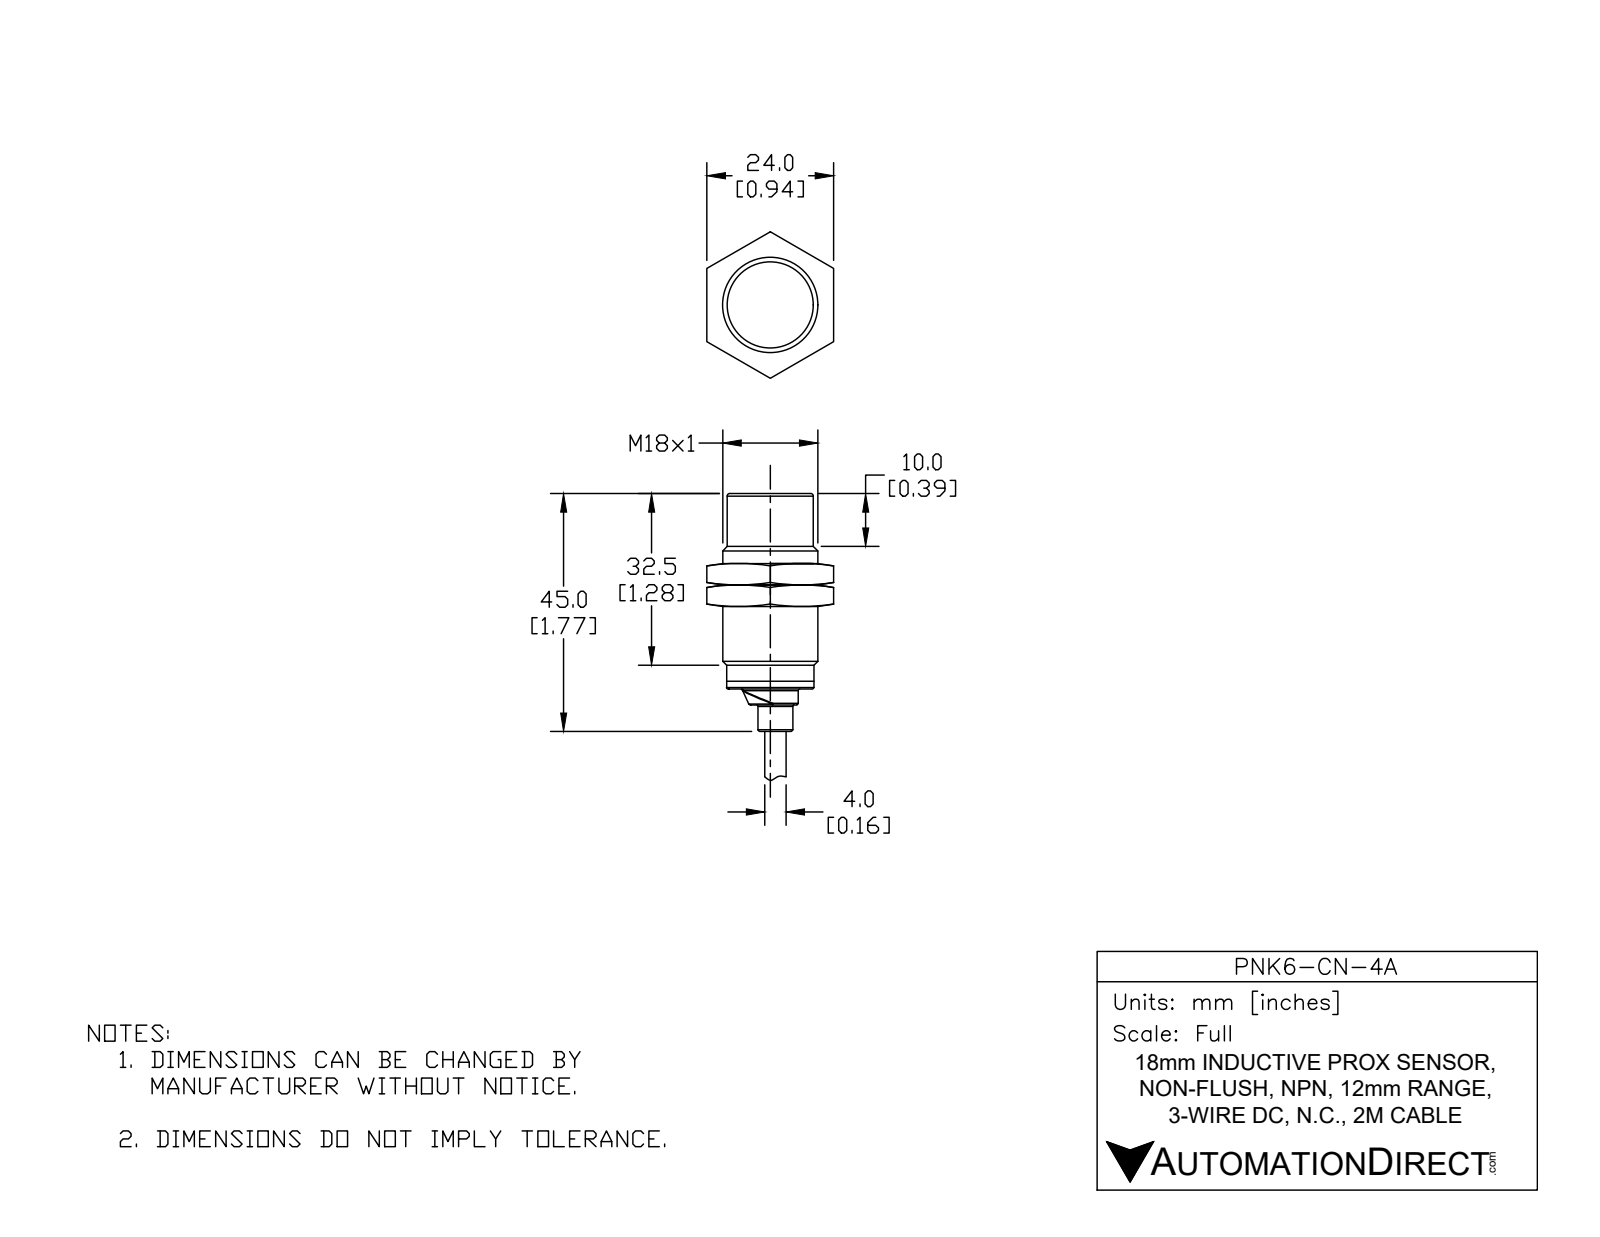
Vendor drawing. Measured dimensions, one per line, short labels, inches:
name: PNK6-CN-4A
written by: SolidWorks 2017 (AUTOMOTIVE_DESIGN)
unit: in
bodies: 1 solid, 78 faces (19 planar, 27 cylindrical, 32 other)
size: 3.272 × 0.709 × 0.709
volume: 0.61 in³; area: 5.425 in²
holes: 1× ⌀0.162
bosses: 6× ⌀0.049, 1× ⌀0.709, 1× ⌀0.65, 1× ⌀0.65, 1× ⌀0.417, 1× ⌀0.26, 1× ⌀0.157
rounds: 1× R0.146
face distances: 1.457, 1.398, 0.059, 1.575, 0.177, 0.118, 1.545, 0.148, 0.089, 0.03
